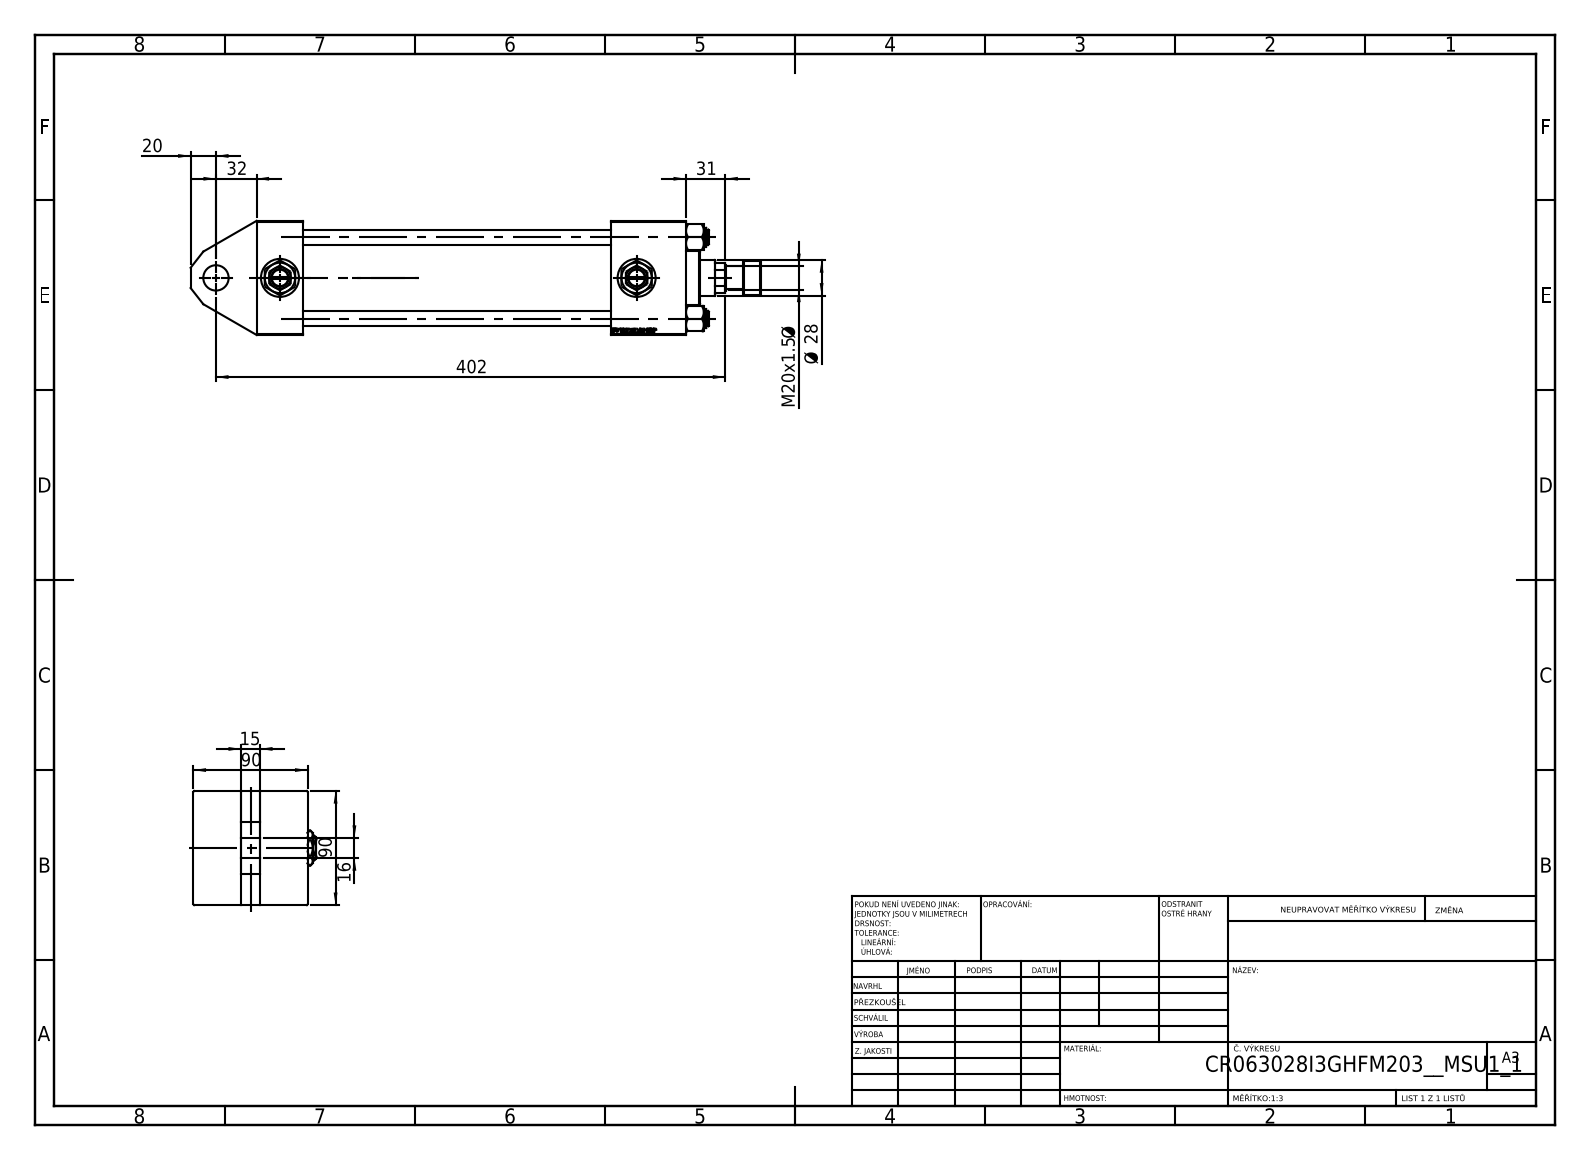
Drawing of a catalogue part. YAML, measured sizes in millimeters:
part_name: "NUT_M5_I; V215CR_VCP_I; V215CR_TYCINKA_I; V215CR_I_Body (+3 more)"
step_written_by: "SolidWorks 2019 (CONFIG_CONTROL_DESIGN)"
units: millimeters
bodies: {solids: 14, faces: 1194, planar: 554, cylindrical: 96, other: 544}
overall_size: [450, 97, 90]
volume: 1315000
surface_area: 317773
round_holes:
  - {diameter: 12, count: 4}
  - {diameter: 7, count: 2}
  - {diameter: 20.96, count: 2}
  - {diameter: 30, count: 2}
  - {diameter: 18.5, count: 1}
  - {diameter: 20, count: 1}
  - {diameter: 28, count: 1}
  - {diameter: 31, count: 1}
  - {diameter: 50, count: 1}
  - {diameter: 60, count: 1}
  - {diameter: 63, count: 1}
round_bosses_or_shafts:
  - {diameter: 15, count: 4}
  - {diameter: 69, count: 1}
  - {diameter: 42, count: 1}
  - {diameter: 27, count: 1}
  - {diameter: 18, count: 1}
face_to_face_distances: [90, 37, 339, 302, 59, 37.5, 52.5, 280, 243, 310.3]
hole_center_spacings: [45.47, 64.3, 90.93, 50.5, 281.5, 332]
